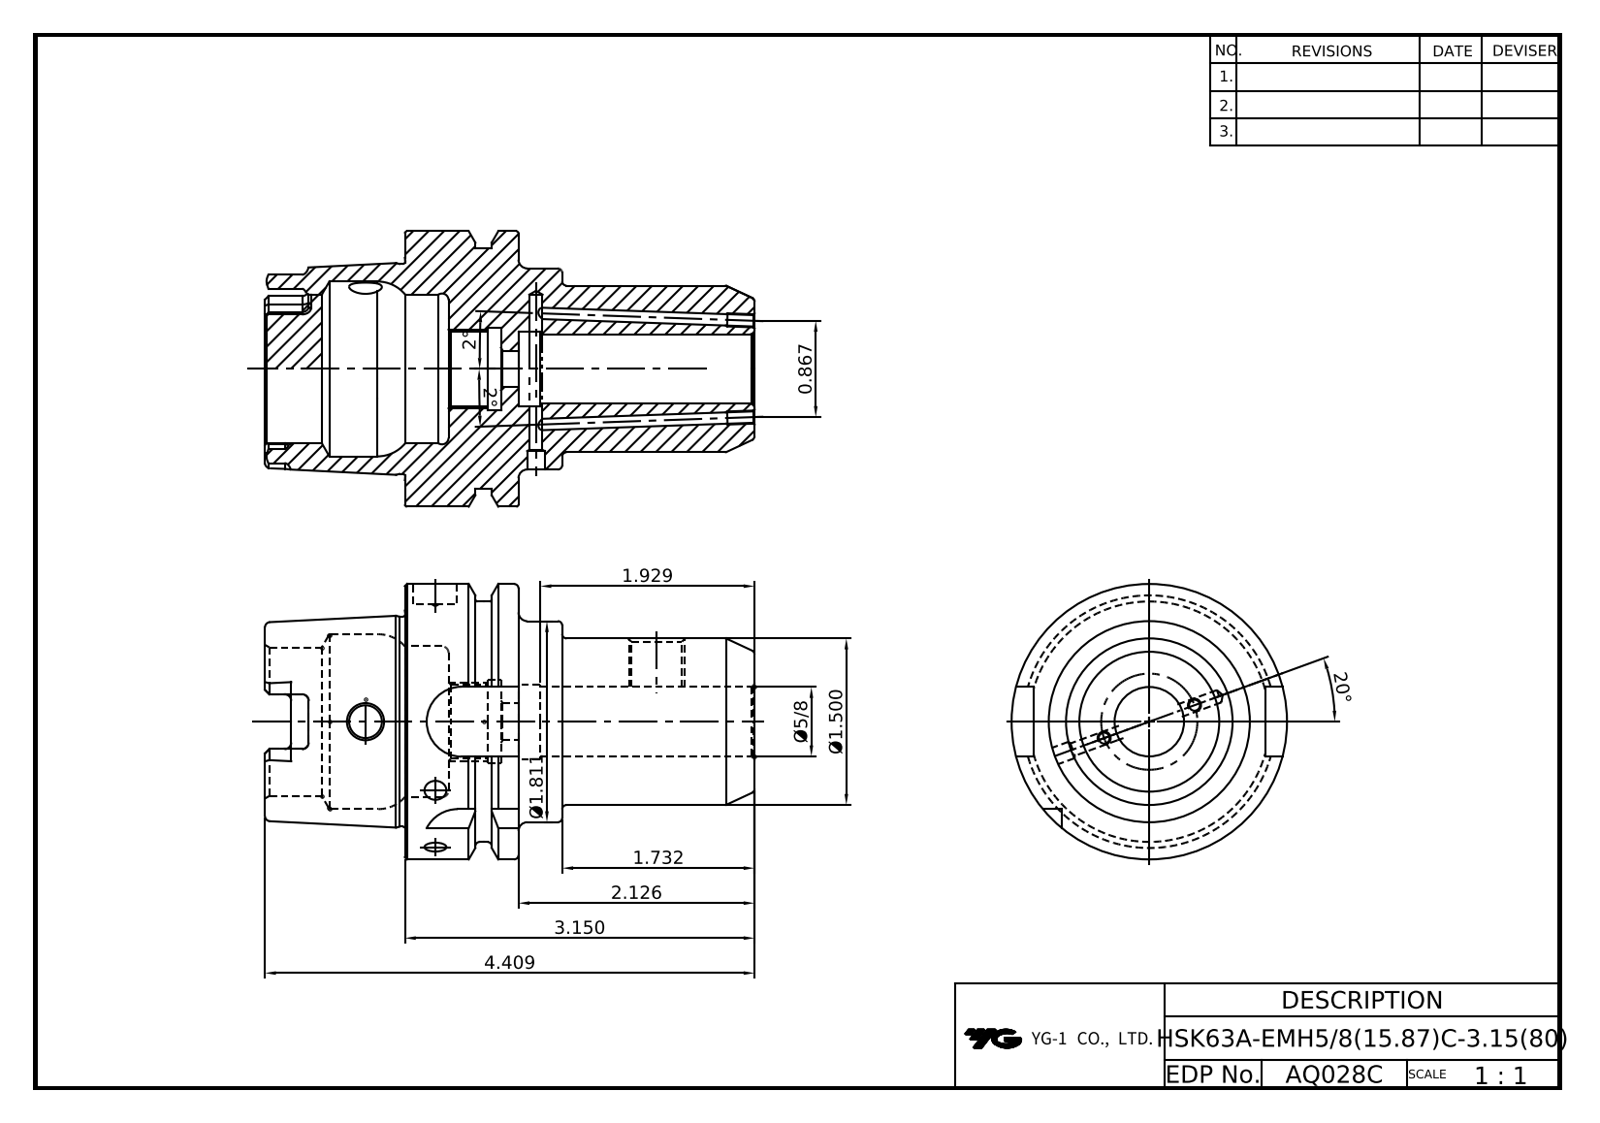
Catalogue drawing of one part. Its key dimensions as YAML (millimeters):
part_name: "LO-HSK63A-EMH15.875C-80"
step_written_by: "Autodesk Inventor 2022 (AUTOMOTIVE_DESIGN)"
units: millimeters
bodies: {solids: 1, faces: 129, planar: 45, cylindrical: 37, other: 47}
overall_size: [112, 63, 63]
volume: 134718
surface_area: 32111
round_holes:
  - {diameter: 2.46, count: 2}
  - {diameter: 7.5, count: 1}
  - {diameter: 8.4, count: 1}
  - {diameter: 10, count: 1}
  - {diameter: 11.33, count: 1}
  - {diameter: 15.88, count: 1}
  - {diameter: 16.92, count: 1}
  - {diameter: 17.07, count: 1}
  - {diameter: 19, count: 1}
  - {diameter: 34, count: 1}
  - {diameter: 40, count: 1}
round_bosses_or_shafts:
  - {diameter: 63, count: 1}
  - {diameter: 55, count: 1}
  - {diameter: 48.04, count: 1}
  - {diameter: 46, count: 1}
  - {diameter: 38.1, count: 1}
partial_cylinders:
  - {radius: 1.5, count: 6}
  - {radius: 2.9, count: 4}
  - {radius: 8, count: 4}
face_to_face_distances: [26, 10, 54, 58, 16, 80, 70, 32, 42, 112]
hole_center_spacings: [50.6]
